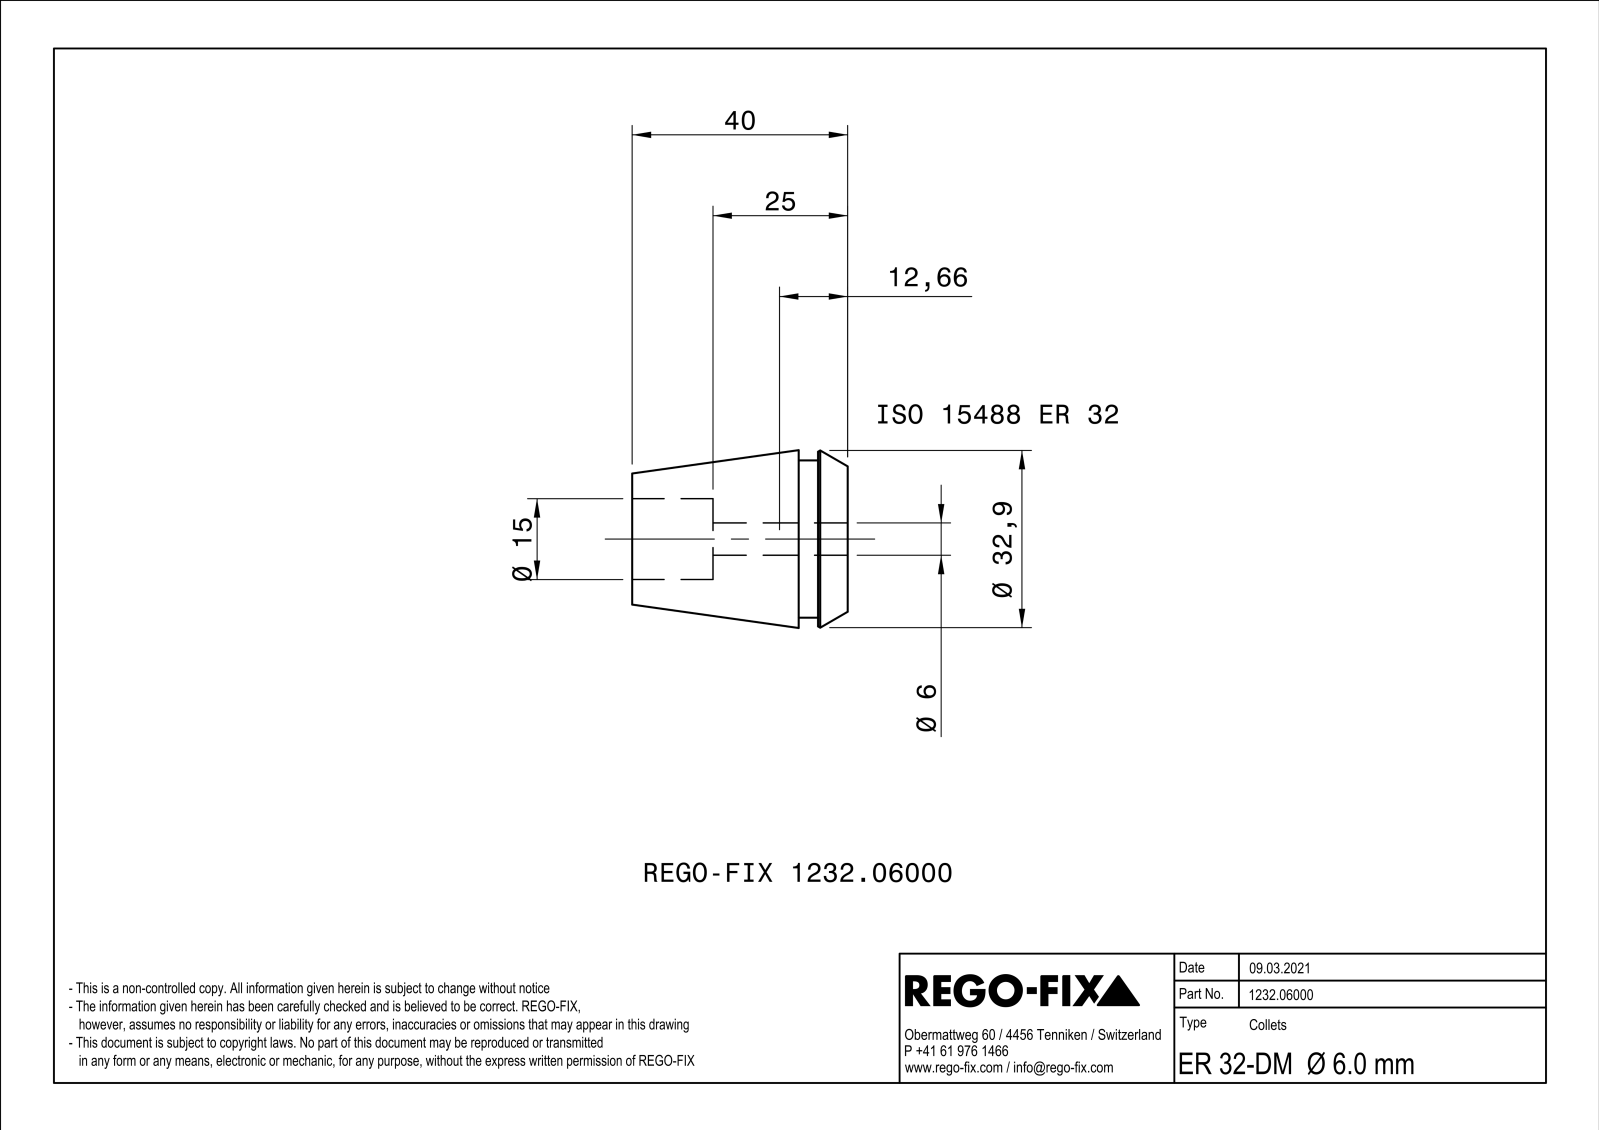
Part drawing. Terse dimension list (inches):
name: NOCUT
written by: SIEMENS PLM Software Solid Edge ST10 (AUTOMOTIVE_DESIGN)
unit: in
bodies: 1 solid, 94 faces (44 planar, 9 cylindrical, 41 other)
size: 1.575 × 1.283 × 1.283
volume: 1.227 in³; area: 14.89 in²
holes: 1× ⌀0.236, 1× ⌀0.591
bosses: 1× ⌀1.15
face distances: 0.031, 1.575, 0.358, 1.217, 0.984, 0.626, 0.591, 0.217, 0.142, 0.768
